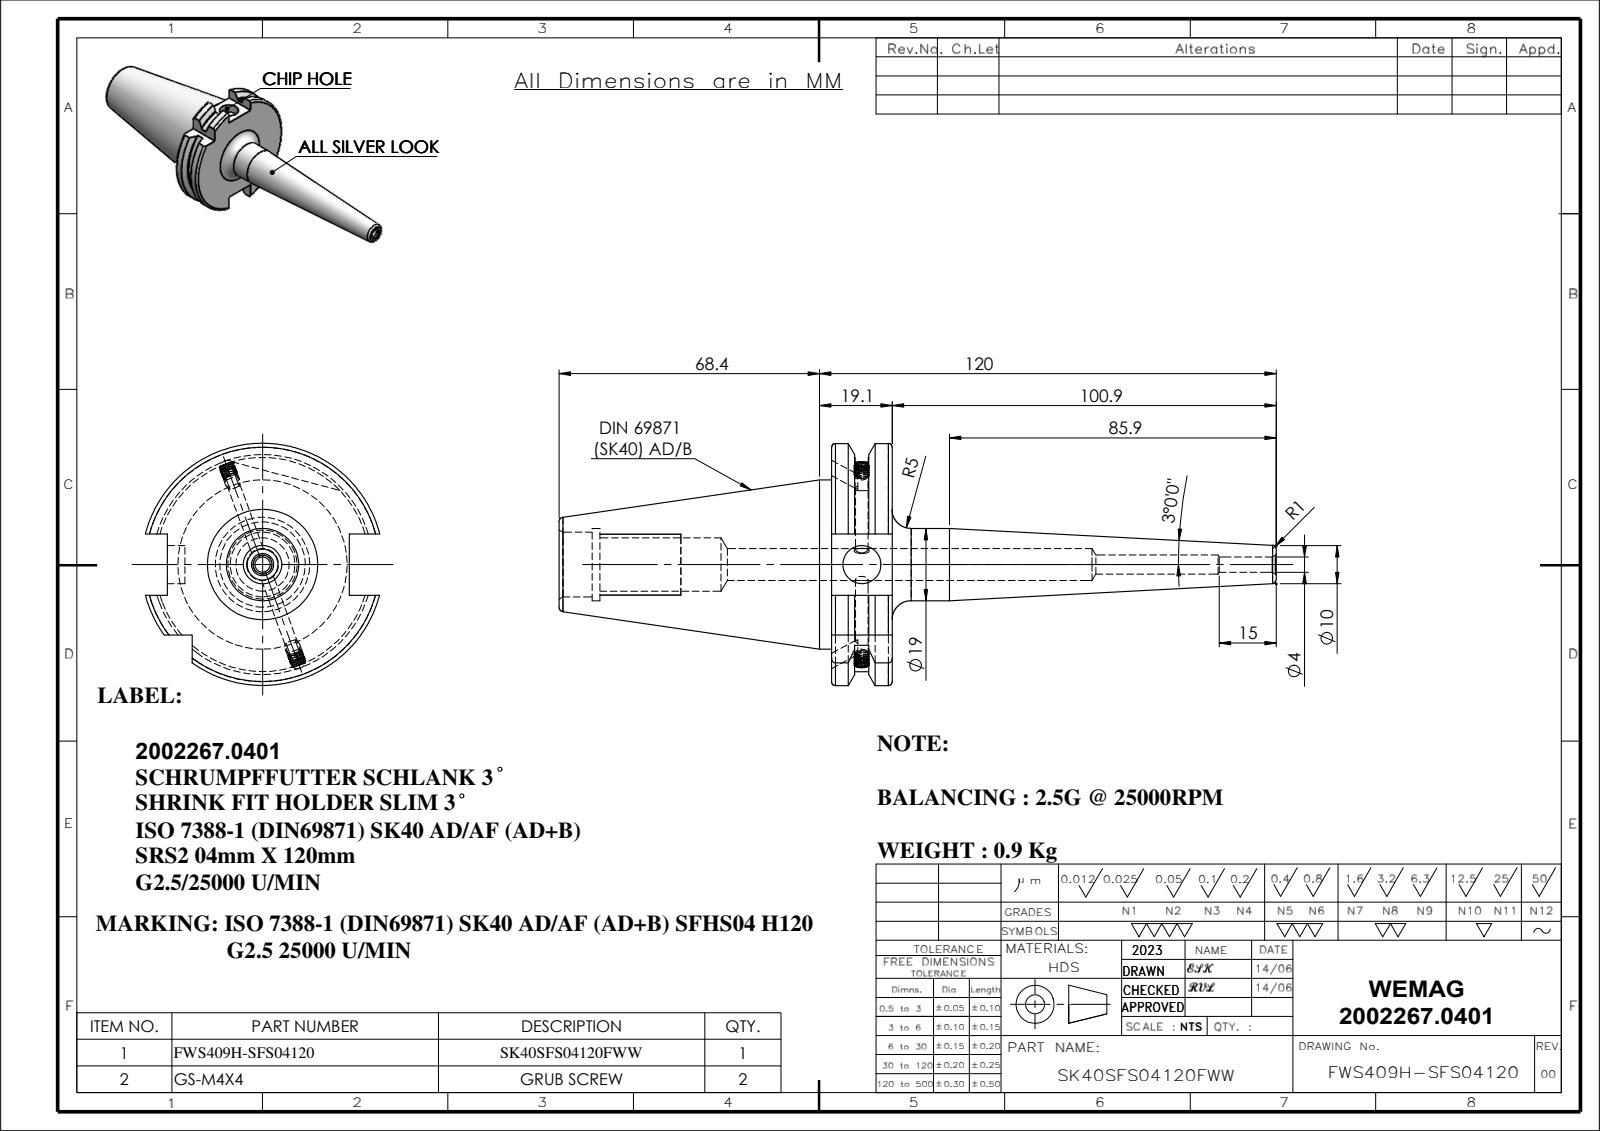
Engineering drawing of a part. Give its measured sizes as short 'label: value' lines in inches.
name: SK40SFS04120FWW; 91406-SRS04120; GS-M4X4_DIN 913 - M4 x 4-N
written by: SolidWorks 2018 (CONFIG_CONTROL_DESIGN)
unit: in
bodies: 3 solids, 198 faces (46 planar, 54 cylindrical, 98 other)
size: 7.417 × 2.502 × 2.42
volume: 7.21 in³; area: 42.68 in²
holes: 1× ⌀0.13, 1× ⌀0.157, 1× ⌀0.197, 1× ⌀0.331, 1× ⌀0.394, 1× ⌀0.551, 1× ⌀0.669, 1× ⌀0.748
bosses: 2× ⌀0.157, 1× ⌀1.75
rounds: 1× R1.107, 1× R1.251
face distances: 0.626, 0.634, 1.882, 2.819, 3.445, 0.421, 2.398, 3.024, 3.056, 2.635
